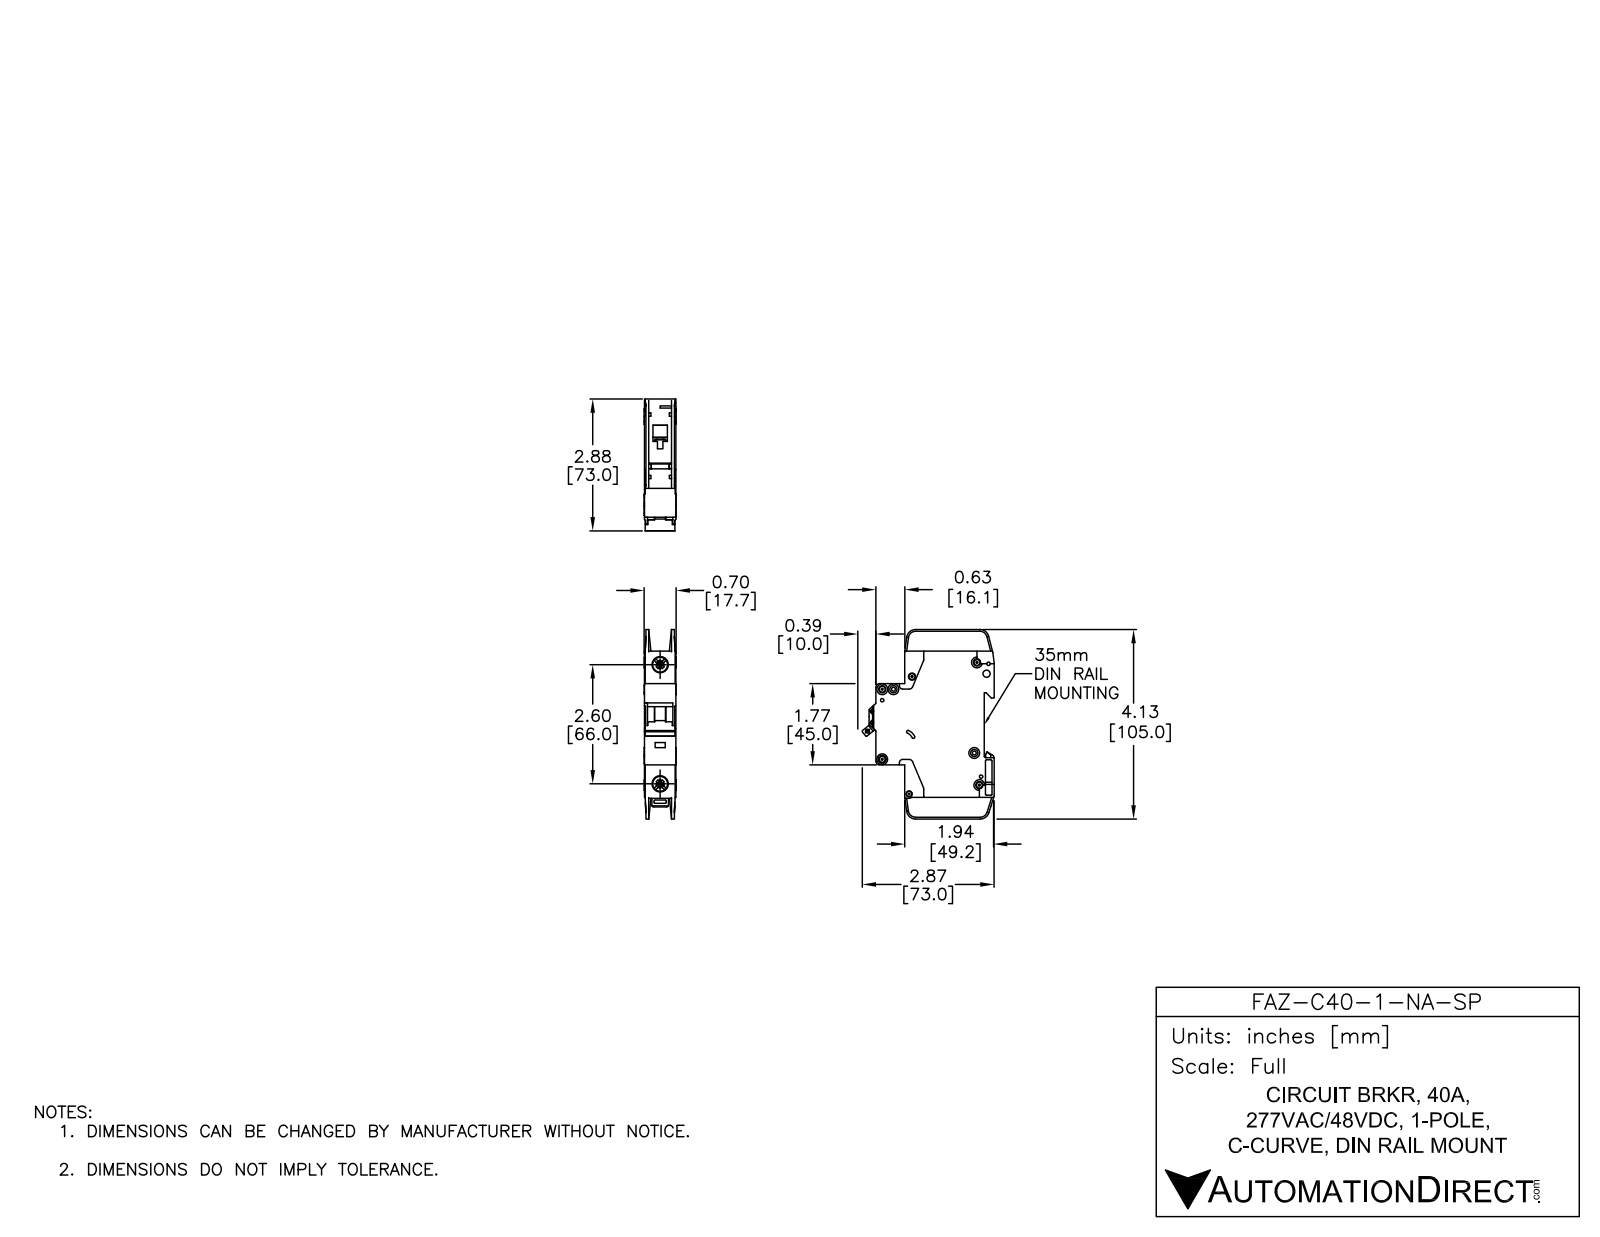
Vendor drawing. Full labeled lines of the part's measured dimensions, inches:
Part name (STEP PRODUCT): FAZ-C40-1-NA-SP
STEP written by: SolidWorks 2014 (AUTOMOTIVE_DESIGN)
Units: inches
Bodies: 3 solids, 784 faces (409 planar, 263 cylindrical, 112 other)
Overall size (bounding box): 4.134 × 2.876 × 0.697
Volume: 4.741 in³ · Surface area: 38.35 in²
Round holes (diameter × count): ⌀0.142 ×7, ⌀0.043 ×2, ⌀0.059 ×2, ⌀0.157 ×2, ⌀0.281 ×2, ⌀0.323 ×2, ⌀0.075 ×1, ⌀0.085 ×1, ⌀0.087 ×1, ⌀0.1 ×1, ⌀0.13 ×1, ⌀0.134 ×1
Round bosses / shafts (diameter × count): ⌀0.236 ×7, ⌀0.098 ×1
Partial cylindrical surfaces — rounded edges, fillets, slot ends (radius × count): R0.01 ×29, R0.02 ×18, R0.039 ×10, R0.079 ×10, R0.197 ×5, R0.157 ×4, R0.071 ×3, R0.008 ×2
Main face-to-face distances: 0.689, 0.593, 0.028, 0.096, 0.069, 0.62, 0.524, 0.551, 0.496, 0.079
Hole centre spacings: 0.244, 0.204, 0.24, 0.322, 0.337, 0.343, 0.437, 0.49
